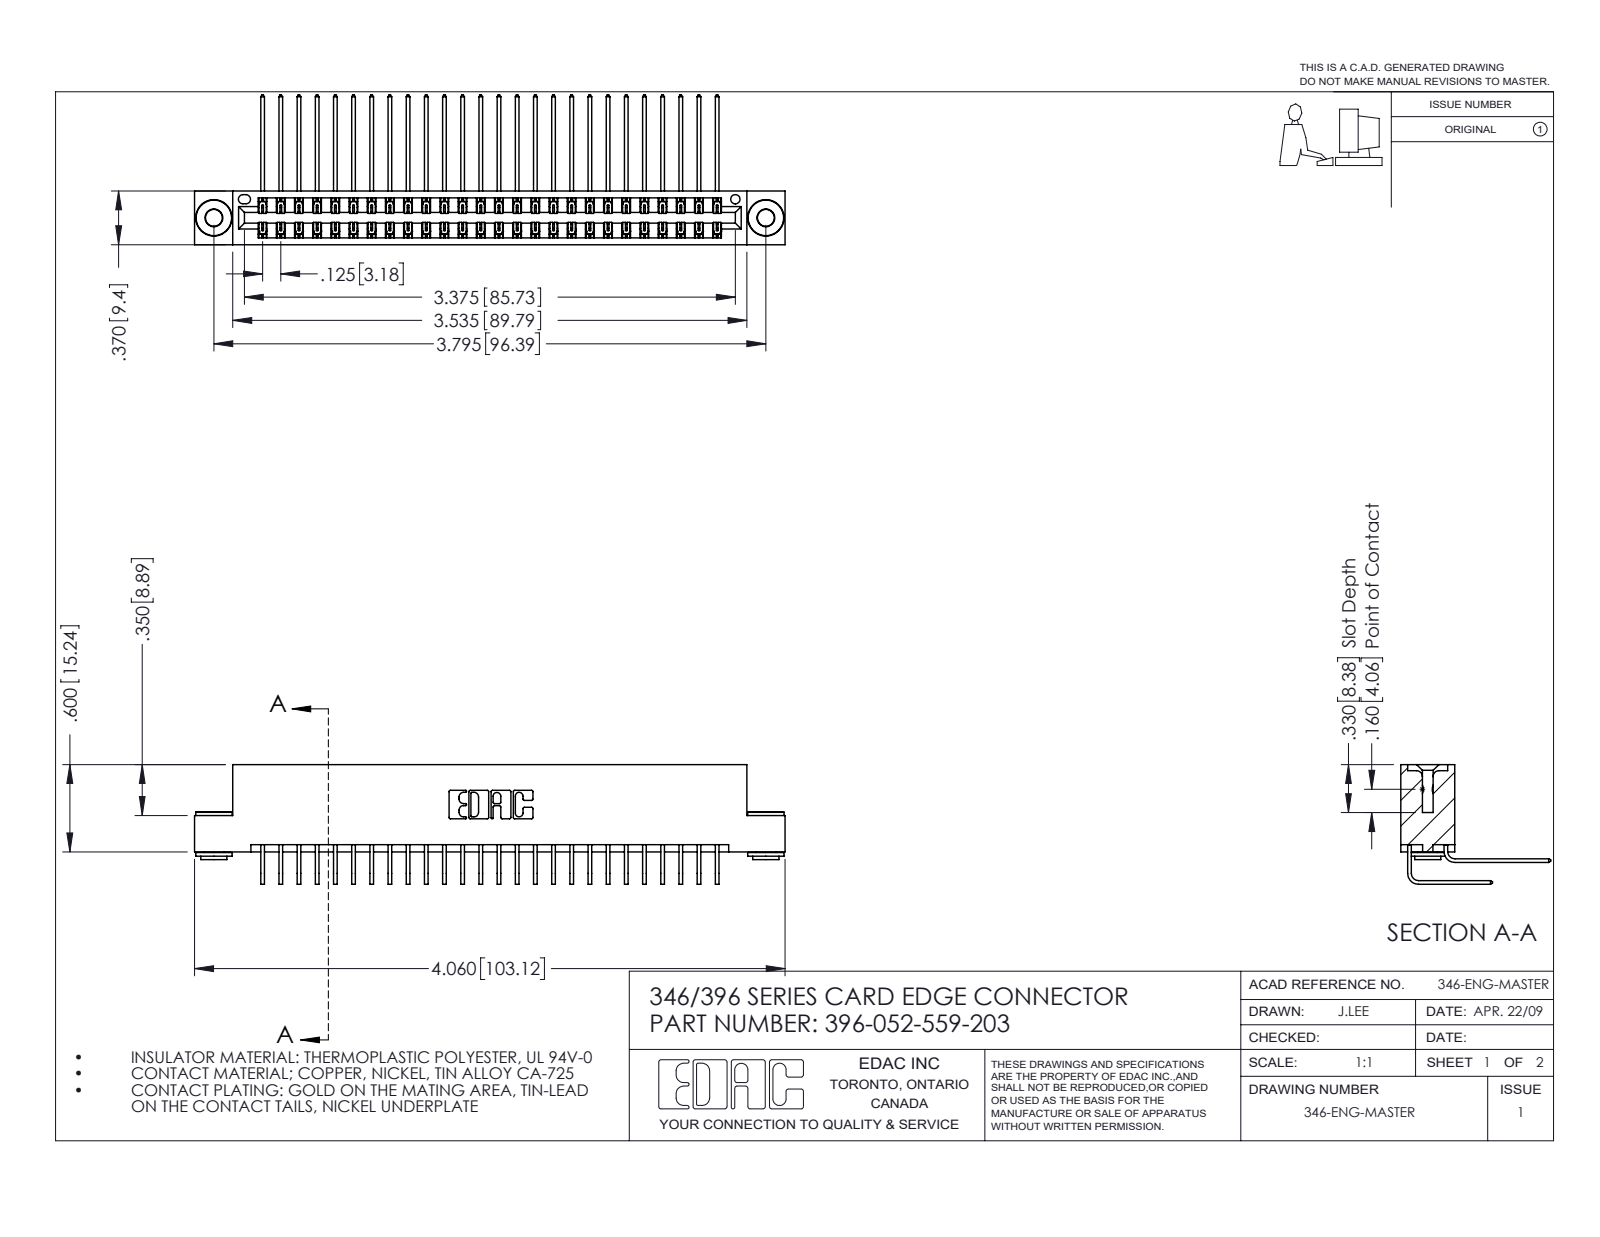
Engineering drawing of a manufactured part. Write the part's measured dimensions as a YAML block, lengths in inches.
part_name: "345-292-001_559 Tail - 2; 396-052-559-203; 346 Part_Flush Mounting Lugs - 0.156 Dia-TH; 345-250-002_345-250-002-102 (+1 more)"
step_written_by: "SolidWorks 2016 (CONFIG_CONTROL_DESIGN)"
units: inches
bodies: {solids: 55, faces: 2968, planar: 2010, cylindrical: 950, other: 8}
overall_size: [4.06, 1.03, 0.823]
volume: 0.626
surface_area: 24.01
round_holes:
  - {diameter: 0.116, count: 2}
  - {diameter: 0.156, count: 2}
  - {diameter: 0.064, count: 1}
round_bosses_or_shafts:
  - {diameter: 0.25, count: 2}
  - {diameter: 0.18, count: 2}
  - {diameter: 0.136, count: 2}
partial_cylinders:
  - {radius: 0.006, count: 78}
  - {radius: 0.01, count: 22}
  - {radius: 0.007, count: 6}
  - {radius: 0.031, count: 6}
  - {radius: 0.026, count: 3}
  - {radius: 0.014, count: 2}
  - {radius: 0.022, count: 2}
  - {radius: 0.024, count: 2}
face_to_face_distances: [0.048, 0.322, 0.25, 0.025, 0.37, 0.072, 0.298, 0.275, 0.148, 0.222]
hole_center_spacings: [0.246, 3.587, 3.795]
